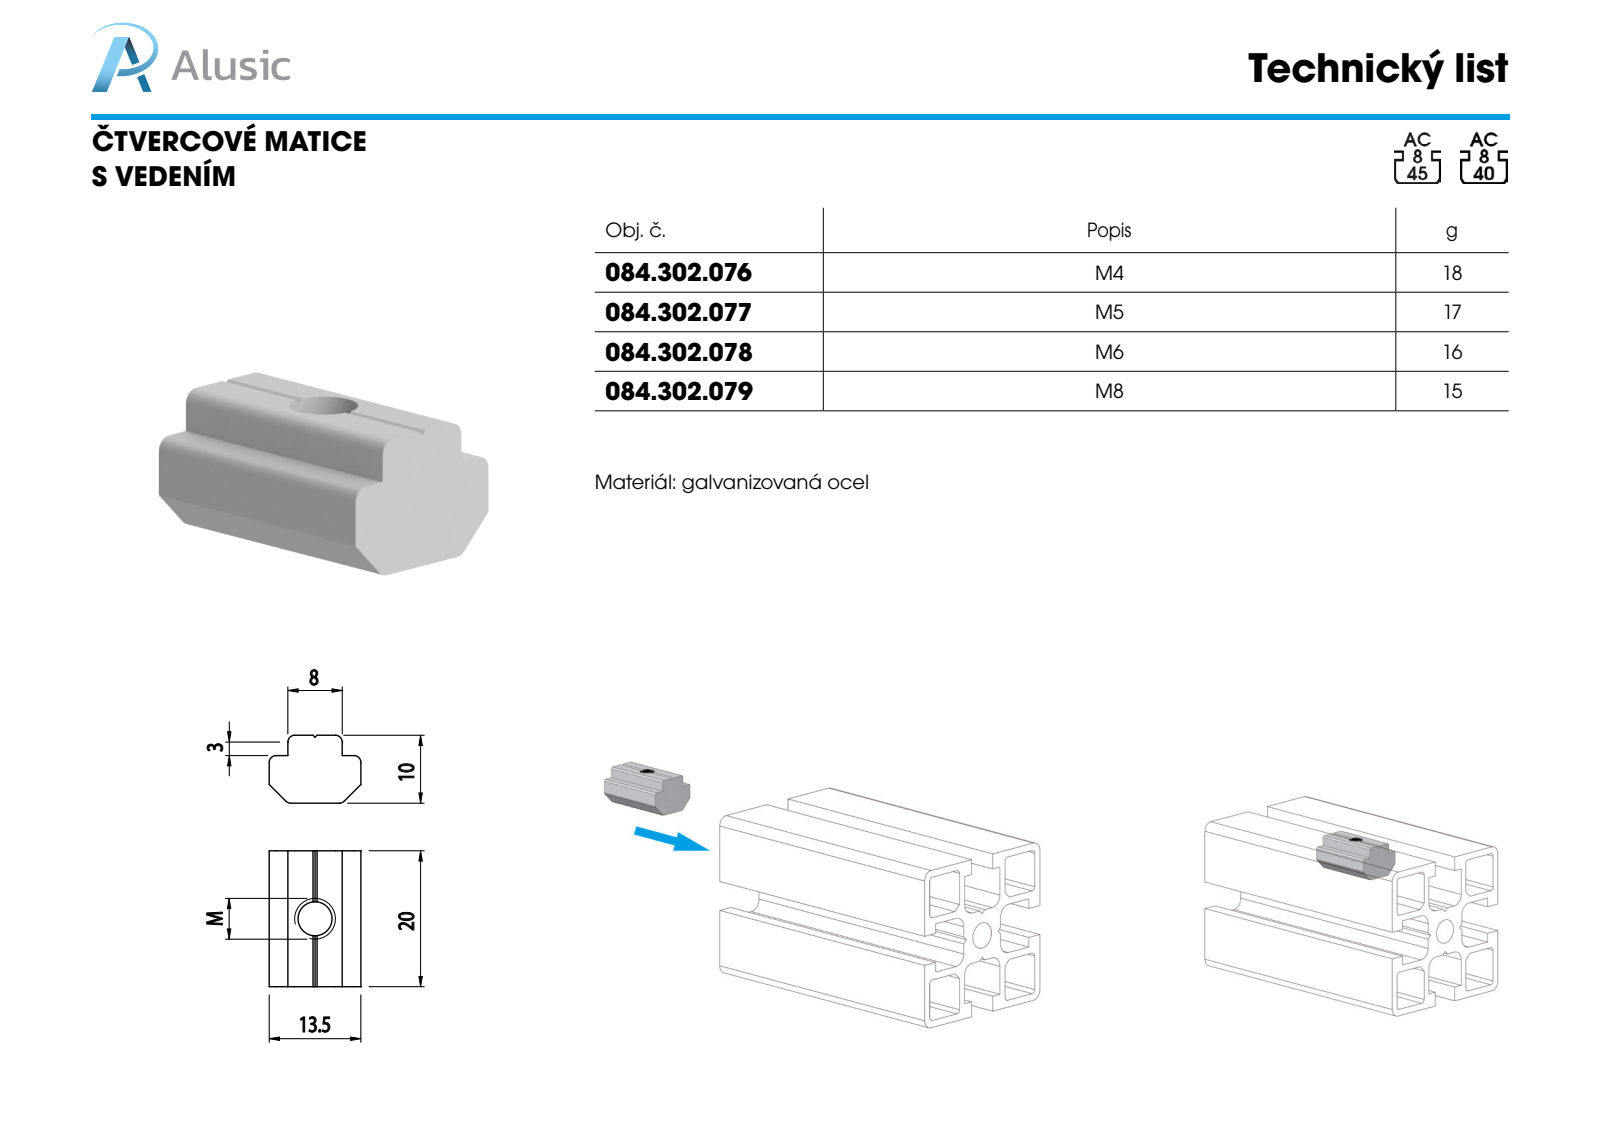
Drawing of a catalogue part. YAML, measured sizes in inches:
part_name: "084.302.078"
step_written_by: "SolidWorks 2012 (CONFIG_CONTROL_DESIGN)"
units: inches
bodies: {solids: 1, faces: 23, planar: 17, cylindrical: 6, other: 0}
overall_size: [0.787, 0.531, 0.382]
volume: 0.119
surface_area: 1.851
round_holes:
  - {diameter: 0.197, count: 1}
partial_cylinders:
  - {radius: 0.02, count: 4}
face_to_face_distances: [0.382, 0.108, 0.423, 0.264, 0.118, 0.787, 0.531, 0.315, 0.368]
